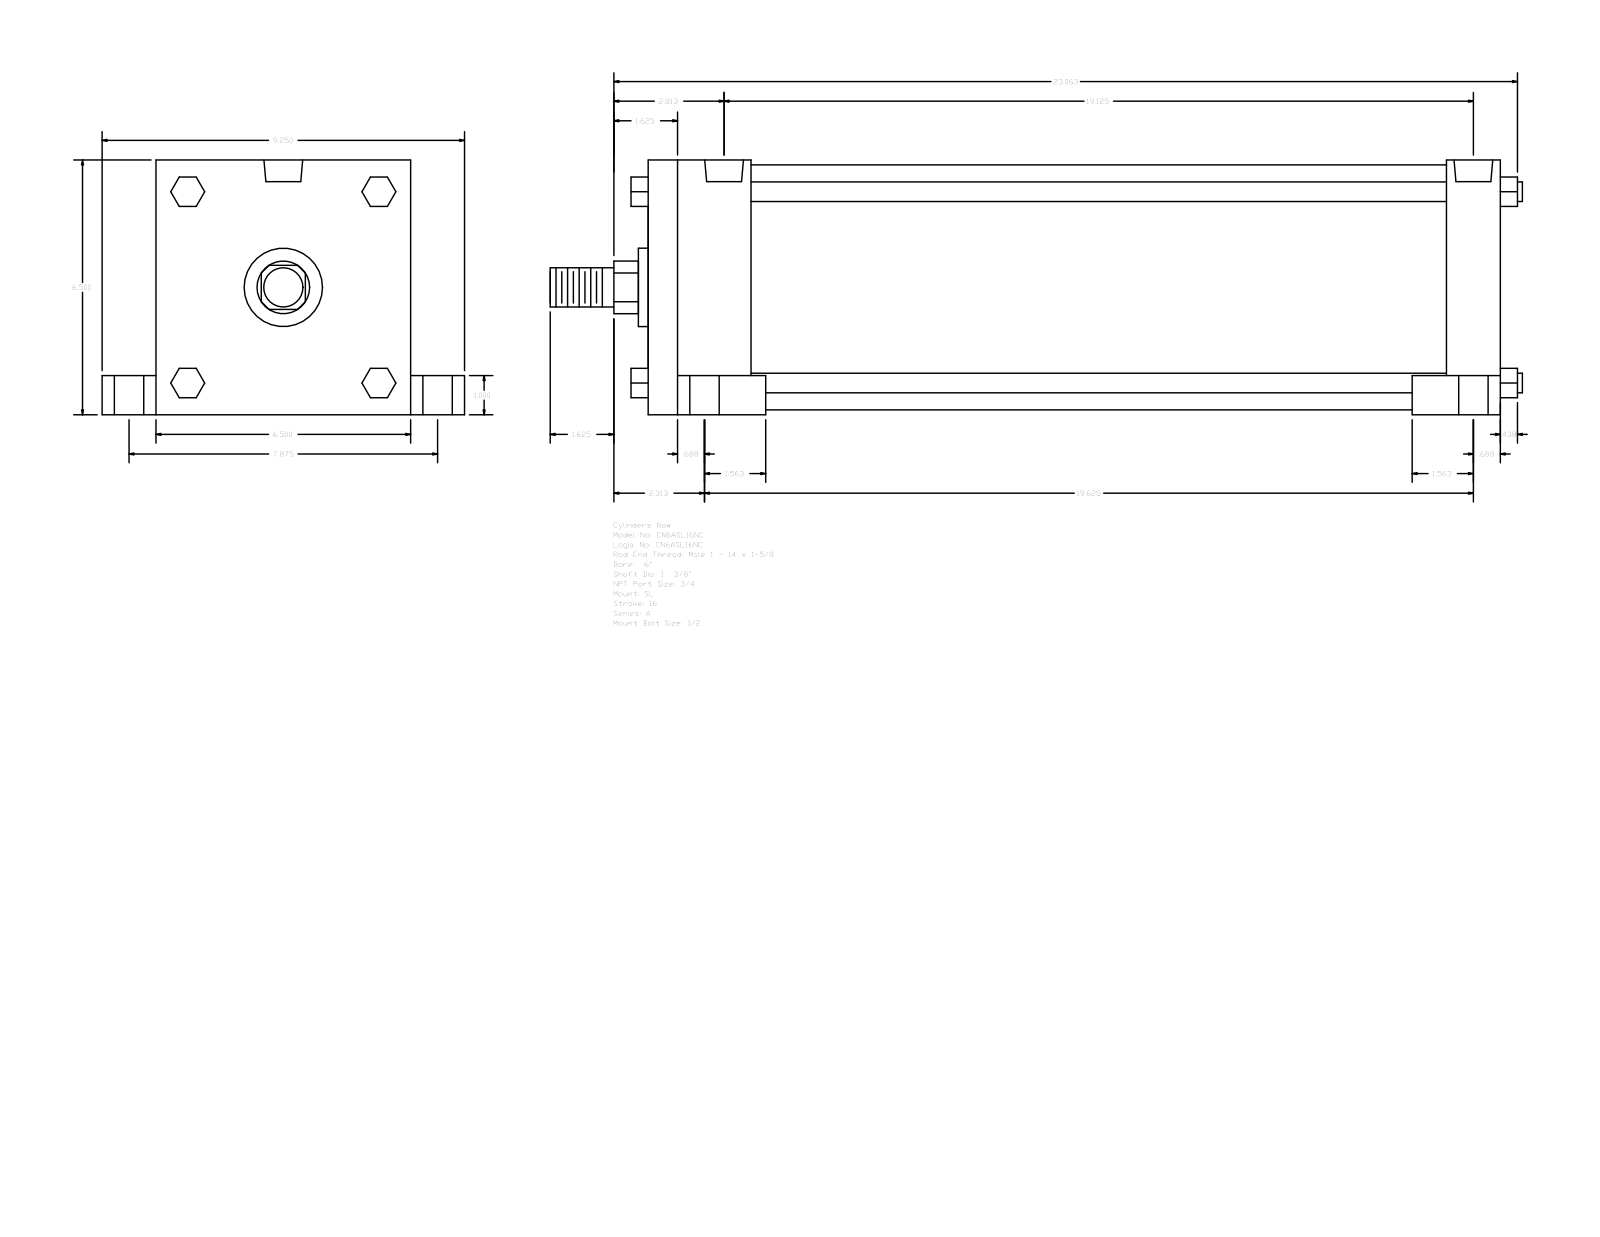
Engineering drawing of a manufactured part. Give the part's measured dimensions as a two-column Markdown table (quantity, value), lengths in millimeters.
| quantity | value |
| --- | --- |
| part name | A_SL__0600_1.375 |
| STEP written by | GSSL Pune (CONFIG_CONTROL_DESIGN) |
| units | millimeters |
| bodies | 0 solids, 150 faces (114 planar, 36 cylindrical, 0 other) |
| overall size | 630.24 × 234.95 × 165.1 |
| round holes (diameter × count) | 15.08 × 4, 19.05 × 4, 25.4 × 4, 25.12 × 2 |
| round bosses / shafts (diameter × count) | 12.7 × 4, 158.75 × 1, 50.8 × 1, 34.92 × 1, 25.4 × 1 |
| partial cylindrical surfaces (radius × count) | 17.06 × 1 |
| main face-to-face distances | 165.1, 552.44, 34.92, 517.52, 66.67, 485.77, 450.85, 25.4, 139.7, 200.02 |
| hole center spacings | 5.56, 100.01, 100.16, 100.81, 101.66, 200.02, 474.65, 480.21 |
